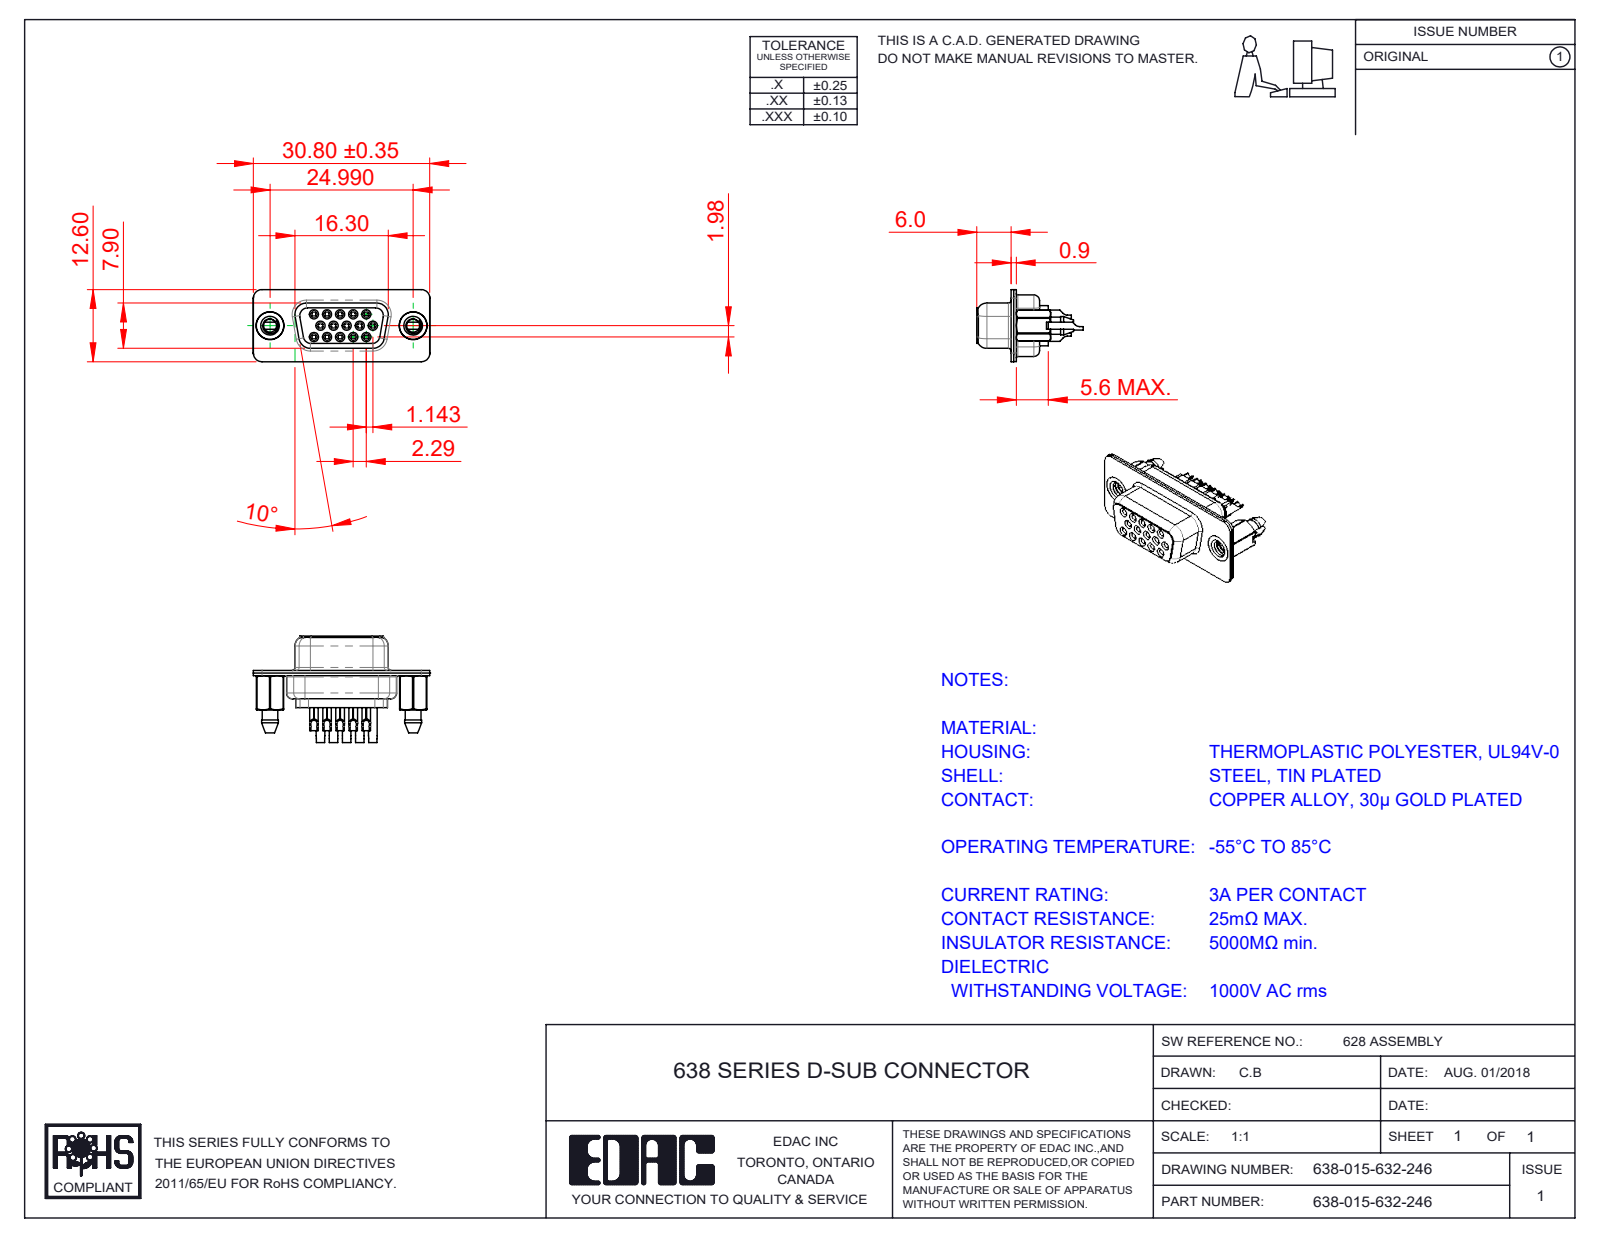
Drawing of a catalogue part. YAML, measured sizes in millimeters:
part_name: "638 Contact Row 2_32; 638 Contact Row 1_32; 638 Contact Row 3_32; 638 4-40 Threaded Boardlock_LP (+4 more)"
step_written_by: "SolidWorks 2020 (CONFIG_CONTROL_DESIGN)"
units: millimeters
bodies: {solids: 20, faces: 1688, planar: 414, cylindrical: 544, other: 730}
overall_size: [30.81, 18.6, 12.6]
volume: 1716
surface_area: 6146
round_holes:
  - {diameter: 0.8, count: 15}
  - {diameter: 1, count: 15}
  - {diameter: 1.1, count: 15}
  - {diameter: 1.6, count: 15}
  - {diameter: 1.7, count: 15}
  - {diameter: 1.8, count: 15}
  - {diameter: 2, count: 2}
  - {diameter: 2.26, count: 2}
  - {diameter: 4, count: 2}
  - {diameter: 4.05, count: 2}
  - {diameter: 4.85, count: 2}
round_bosses_or_shafts:
  - {diameter: 2, count: 15}
  - {diameter: 1.5, count: 15}
  - {diameter: 1.2, count: 15}
  - {diameter: 4.95, count: 2}
  - {diameter: 4.8, count: 2}
partial_cylinders:
  - {radius: 1.5, count: 22}
  - {radius: 2, count: 12}
  - {radius: 0.28, count: 10}
  - {radius: 1.55, count: 8}
  - {radius: 1, count: 7}
  - {radius: 1.35, count: 5}
  - {radius: 0.25, count: 4}
  - {radius: 0.5, count: 4}
face_to_face_distances: [0.45, 0.9, 0.4, 1.43, 8.88, 6.6, 1.4, 6, 2.28, 4.76]
hole_center_spacings: [3.96, 2.28, 4.57, 2.29, 6.05, 6.04, 6.86, 7.92]
